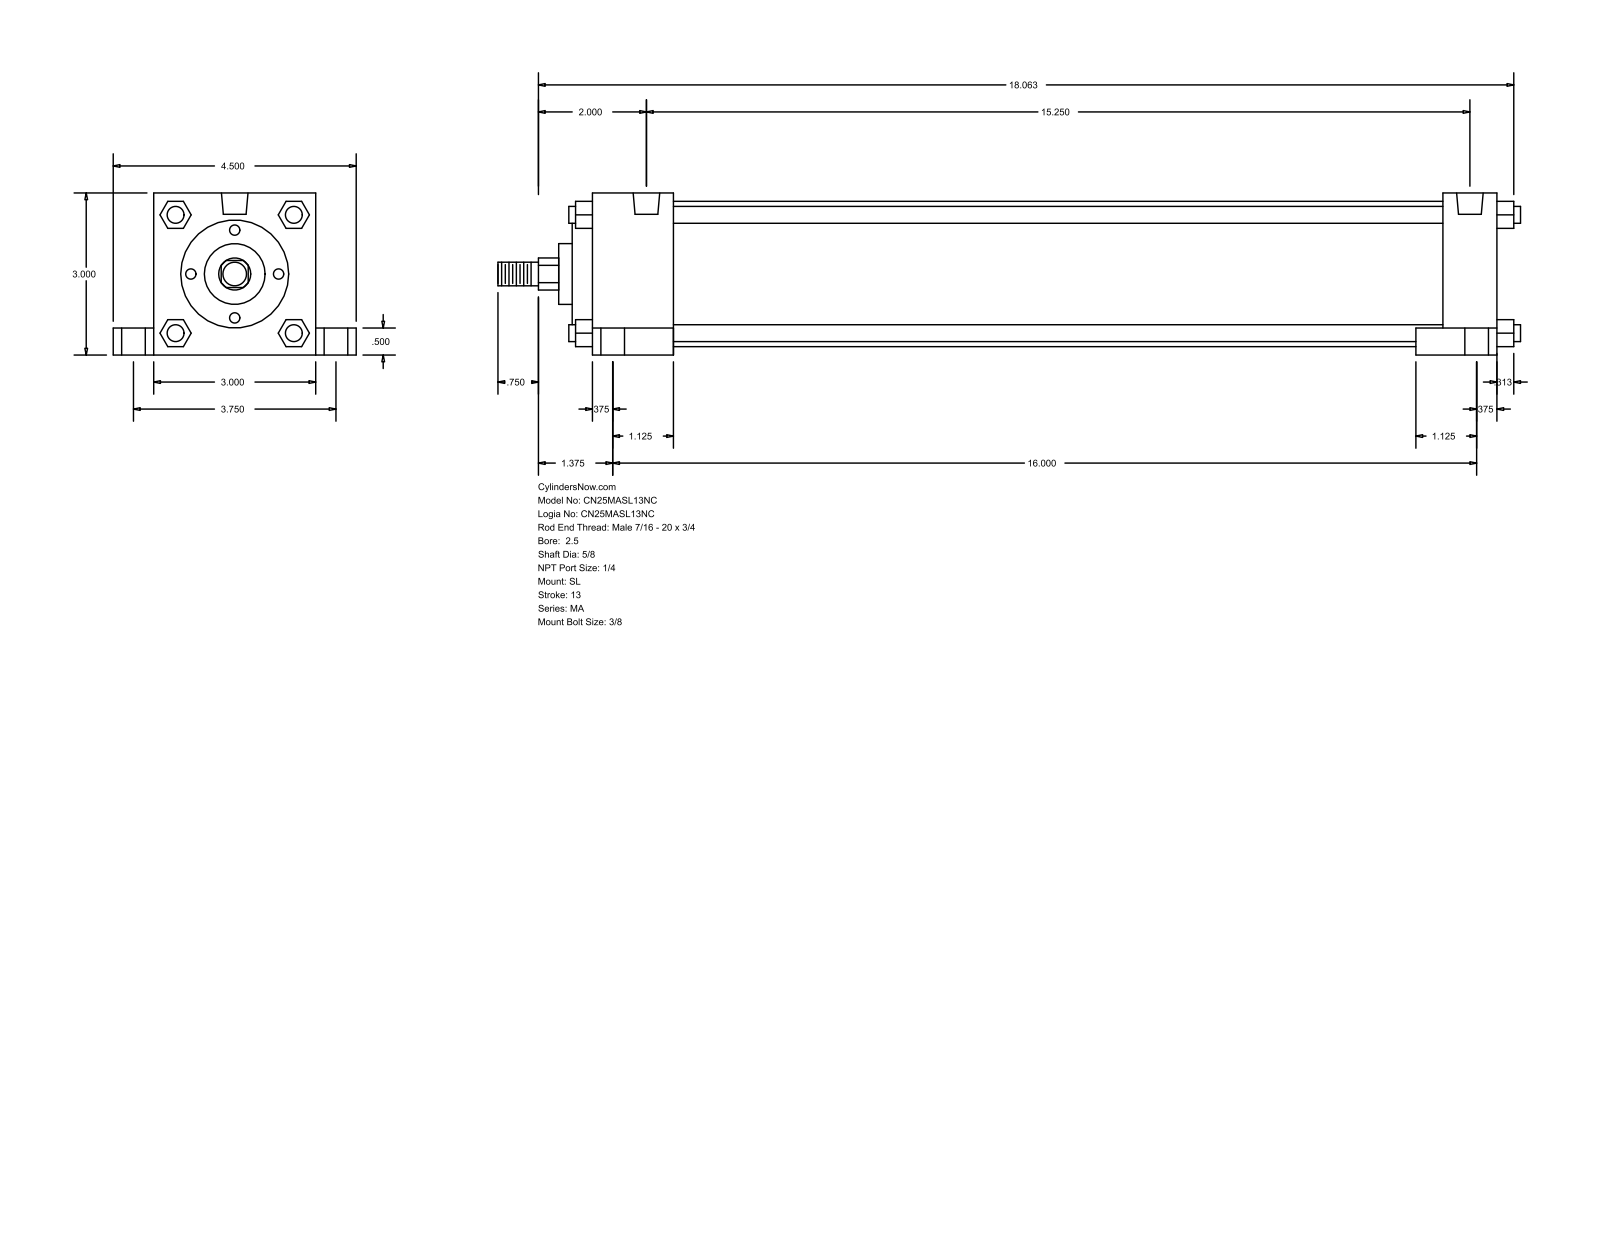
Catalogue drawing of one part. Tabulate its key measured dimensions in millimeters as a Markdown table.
| quantity | value |
| --- | --- |
| part name | MA_SL__0250_0.625 |
| STEP written by | GSSL Pune (CONFIG_CONTROL_DESIGN) |
| units | millimeters |
| bodies | 0 solids, 150 faces (113 planar, 37 cylindrical, 0 other) |
| overall size | 481.01 × 114.3 × 76.2 |
| round holes (diameter × count) | 7.94 × 4, 11.11 × 4, 17.46 × 4, 12.49 × 2 |
| round bosses / shafts (diameter × count) | 7.94 × 4, 68.33 × 1, 50.8 × 1, 28.57 × 1, 15.88 × 1, 11.11 × 1 |
| partial cylindrical surfaces (radius × count) | 7.54 × 1 |
| main face-to-face distances | 76.2, 425.45, 12.7, 361.95, 25.4, 38.1, 387.35, 400.05, 19.05, 63.5 |
| hole center spacings | 47.73, 50.2, 95.24, 387.35, 393.41, 406.03, 406.4, 417.41 |
